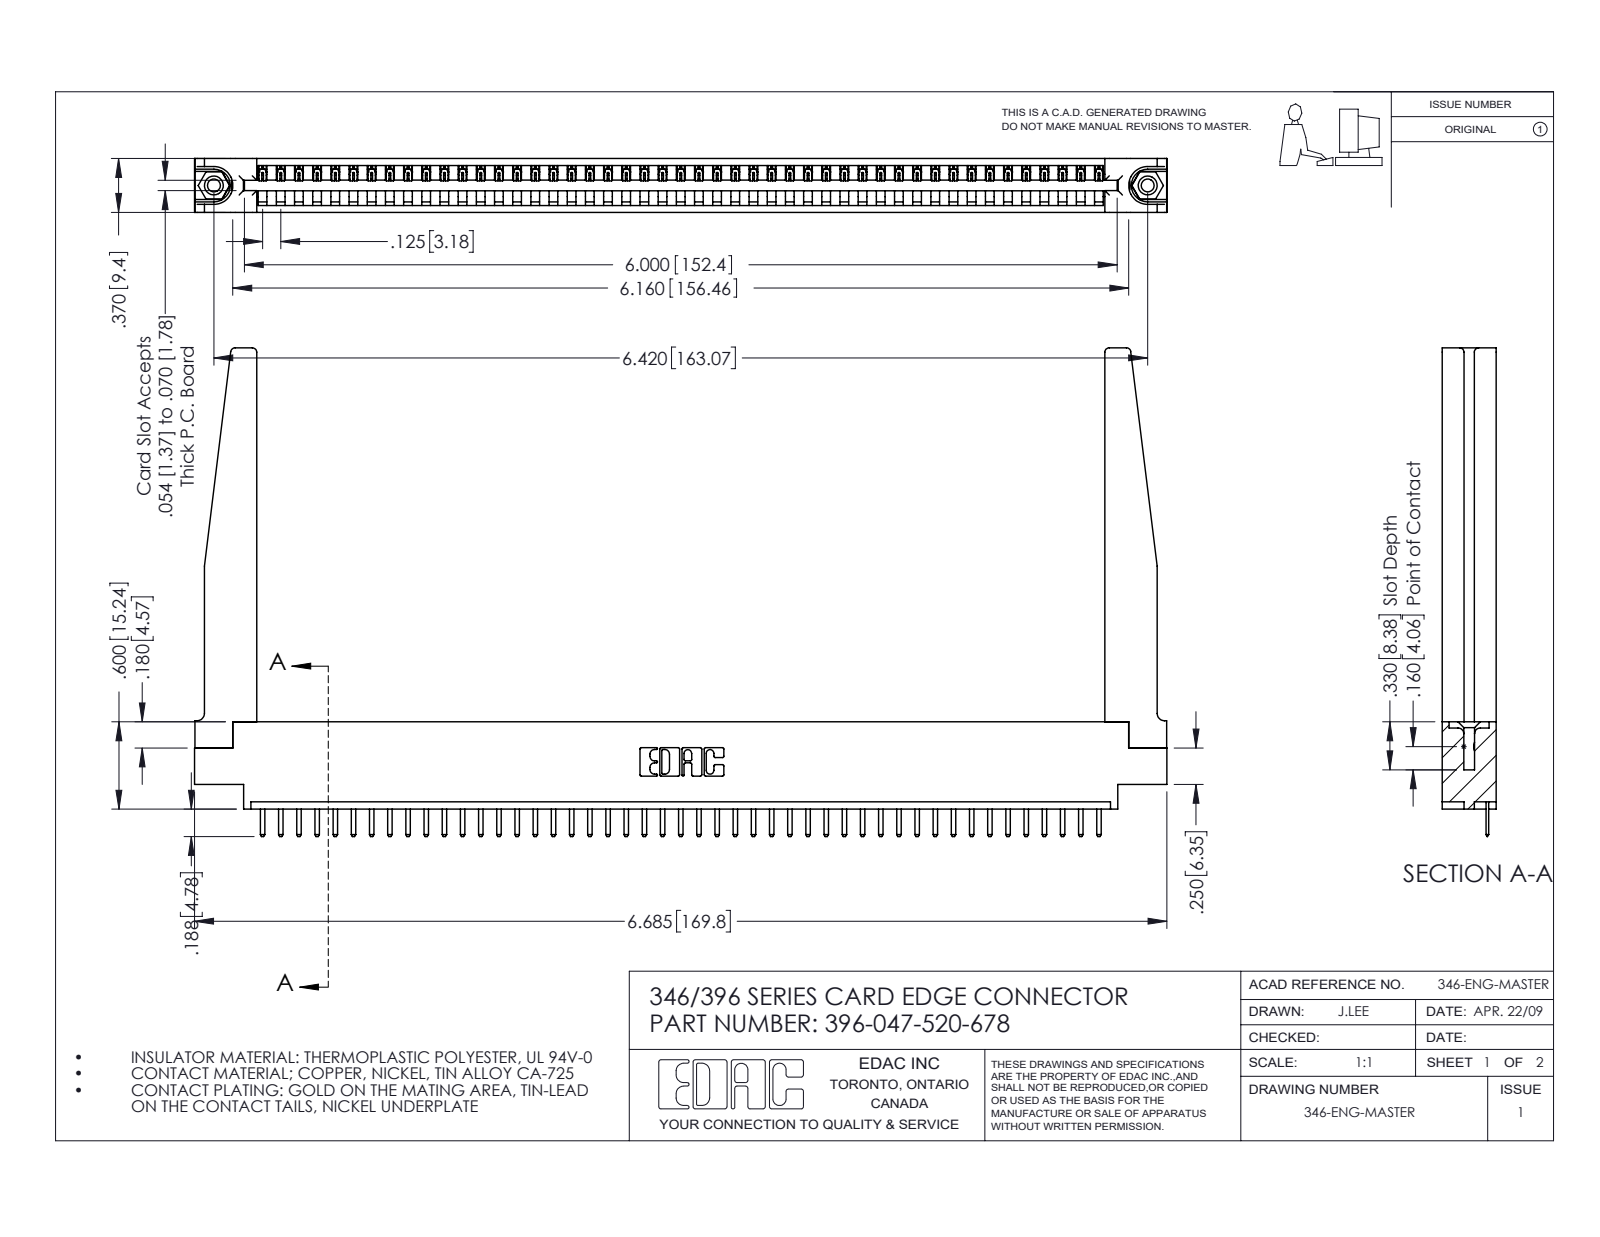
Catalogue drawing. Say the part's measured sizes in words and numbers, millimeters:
The part is named "345-292-001_345-293-120; 345-250-001_345-250-001-102; 346-220-078_345-220-078; 396-047-520-678 (+1 more)". Its 3-D file was written by "SolidWorks 2016 (CONFIG_CONTROL_DESIGN)". It is 52 solids with 3274 faces: 2196 planar, 1026 cylindrical and 52 other. Overall it measures 169.8 by 85.3 by 9.4 millimeters. Its volume is 22 910 cubic millimeters and its surface area 26 300 square millimeters. Round holes: 2 of diameter 2.3, 2 of diameter 3.2, 2 of diameter 4, 1 of diameter 1.6. Round bosses or shafts: 2 of diameter 3.9. Partial cylindrical surfaces (rounded edges, fillets, slot ends): 96 of radius 0.3, 94 of radius 0.2, 22 of radius 0.3, 8 of radius 0.8, 6 of radius 0.2, 6 of radius 0.8, 3 of radius 0.7, 2 of radius 0.8. The main face-to-face distances are 9.4, 1.2, 8.2, 3.8, 1.8, 3.8, 6.4, 5.6, 2.5, 4.4. The hole center spacings are 6.2, 157.8, 163.1.
